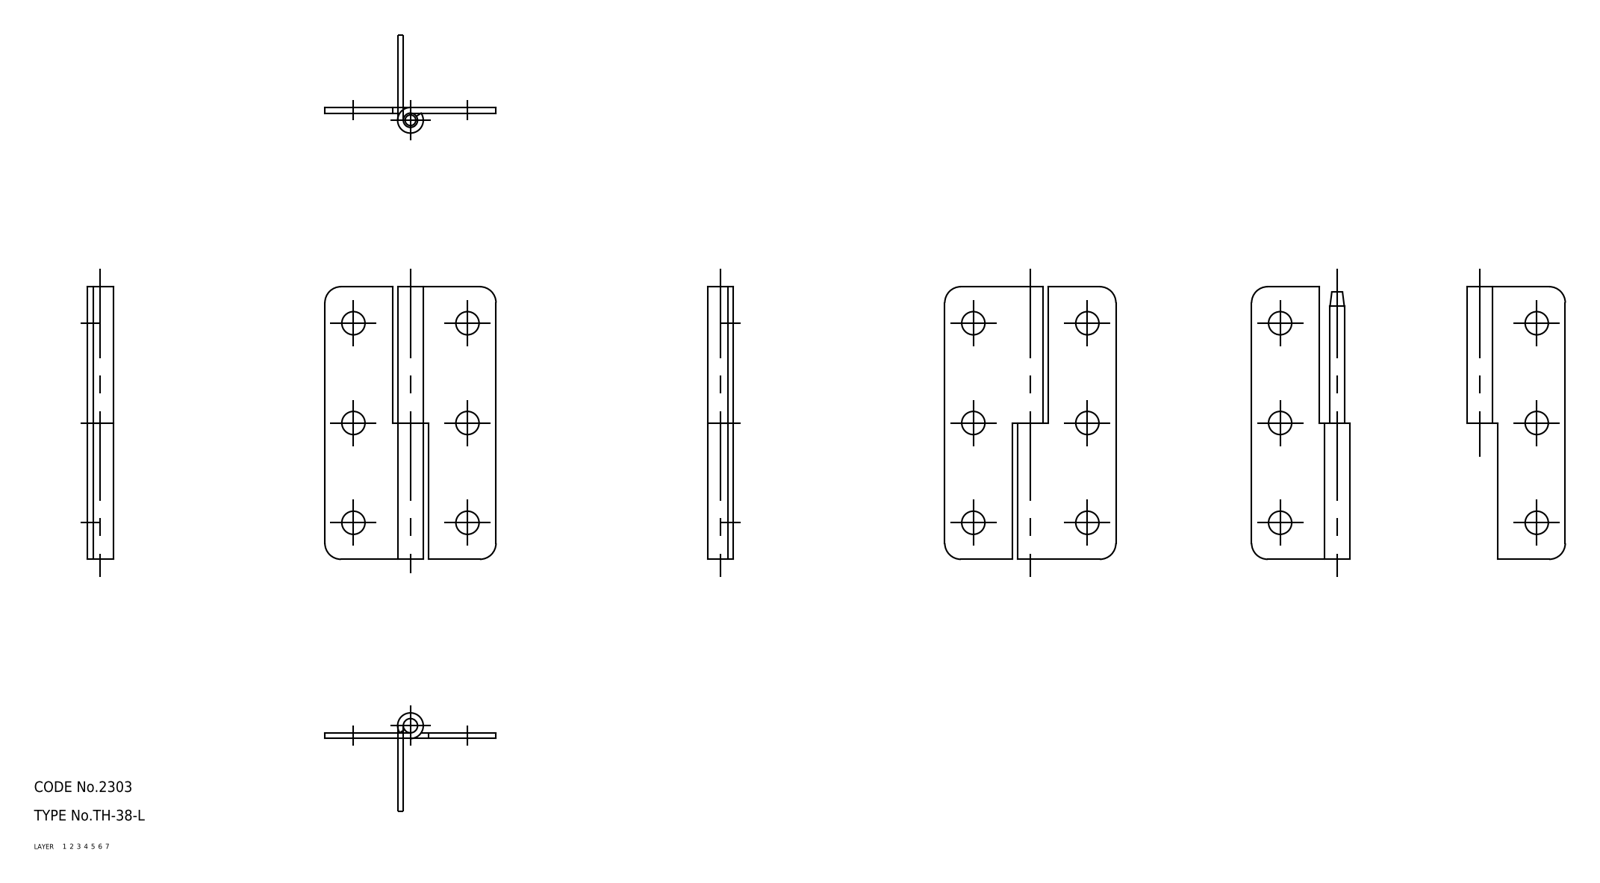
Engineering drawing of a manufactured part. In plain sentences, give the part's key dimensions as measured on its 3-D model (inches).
The part is named "shaft; hinge piece_B; hinge piece_A; TH_38_L_8552_36". Its 3-D file was written by "CADfix (AUTOMOTIVE_DESIGN)". It is 3 solids with 42 faces: 0 planar, 0 cylindrical and 42 other. Overall it measures 3.012 by 1.89 by 0.283 inches. Its volume is 0.467 cubic inches and its surface area 15.95 square inches.
